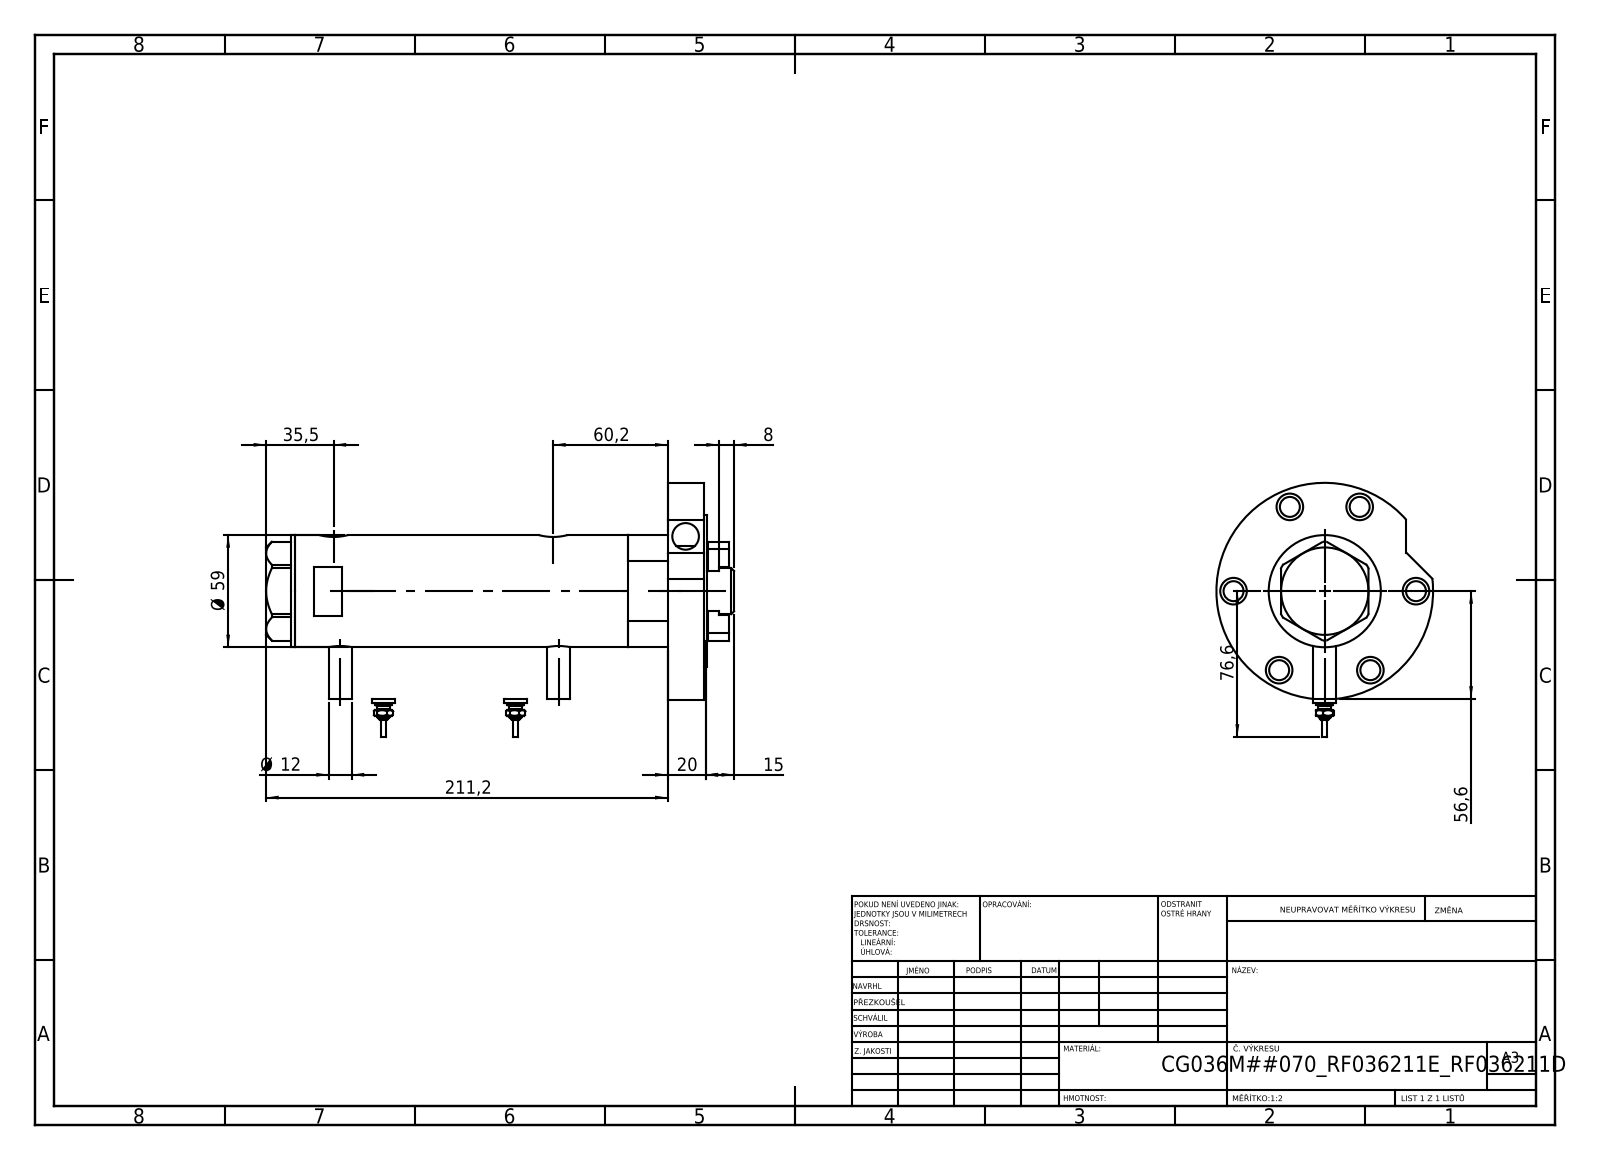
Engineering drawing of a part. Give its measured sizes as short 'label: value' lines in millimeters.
name: V270CG_VC; V270CG_MIDDLE; Switch; V270CG_BACK (+3 more)
written by: SolidWorks 2019 (CONFIG_CONTROL_DESIGN)
unit: mm
bodies: 9 solids, 296 faces (114 planar, 118 cylindrical, 64 other)
size: 246.2 × 133.6 × 114
volume: 711 054 mm³; area: 154 119 mm²
holes: 10× ⌀10.5, 7× ⌀14, 4× ⌀6.1, 2× ⌀9.73, 2× ⌀12.5, 2× ⌀15, 1× ⌀8.5, 1× ⌀25, 1× ⌀26.5, 1× ⌀36, 1× ⌀40, 1× ⌀48
bosses: 4× ⌀12, 2× ⌀9, 2× ⌀7, 2× ⌀4.5, 2× ⌀2.5, 1× ⌀114, 1× ⌀80, 1× ⌀59
face distances: 2, 19, 21, 217.2, 196.2, 215.2, 137.2, 59, 78, 80
hole spacings: 48, 19.92, 46.09, 57.24, 12, 28.22, 28.88, 35.17
